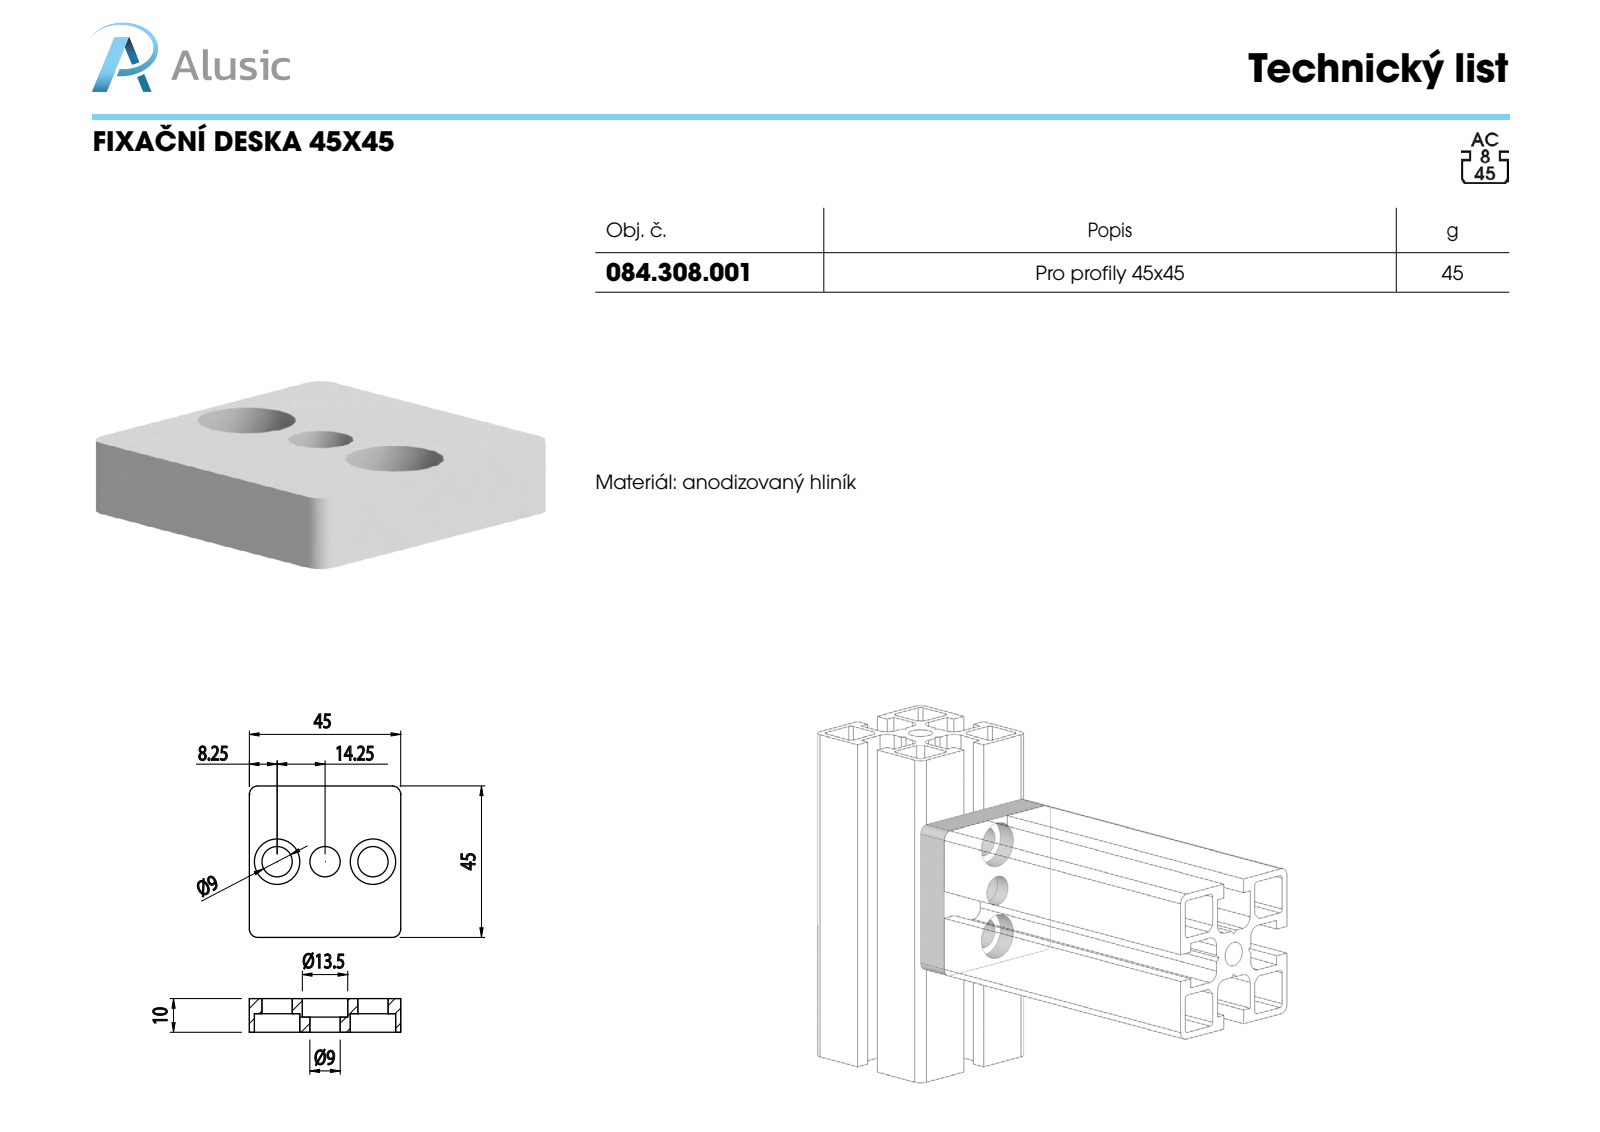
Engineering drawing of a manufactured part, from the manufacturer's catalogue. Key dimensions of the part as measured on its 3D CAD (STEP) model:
Part name (STEP PRODUCT): 084.308.001
STEP written by: SolidWorks 2011 (CONFIG_CONTROL_DESIGN)
Units: millimetres
Bodies: 1 solid, 25 faces (9 planar, 16 cylindrical, 0 other)
Overall size (bounding box): 45 × 45 × 10
Volume: 16 976 mm³ · Surface area: 6 496 mm²
Round holes (diameter × count): ⌀9 ×3, ⌀13.5 ×3
Partial cylindrical surfaces — rounded edges, fillets, slot ends (radius × count): R2.5 ×4
Main face-to-face distances: 10, 45, 4.5, 5.5, 1
Hole centre spacings: 14.25, 28.5
